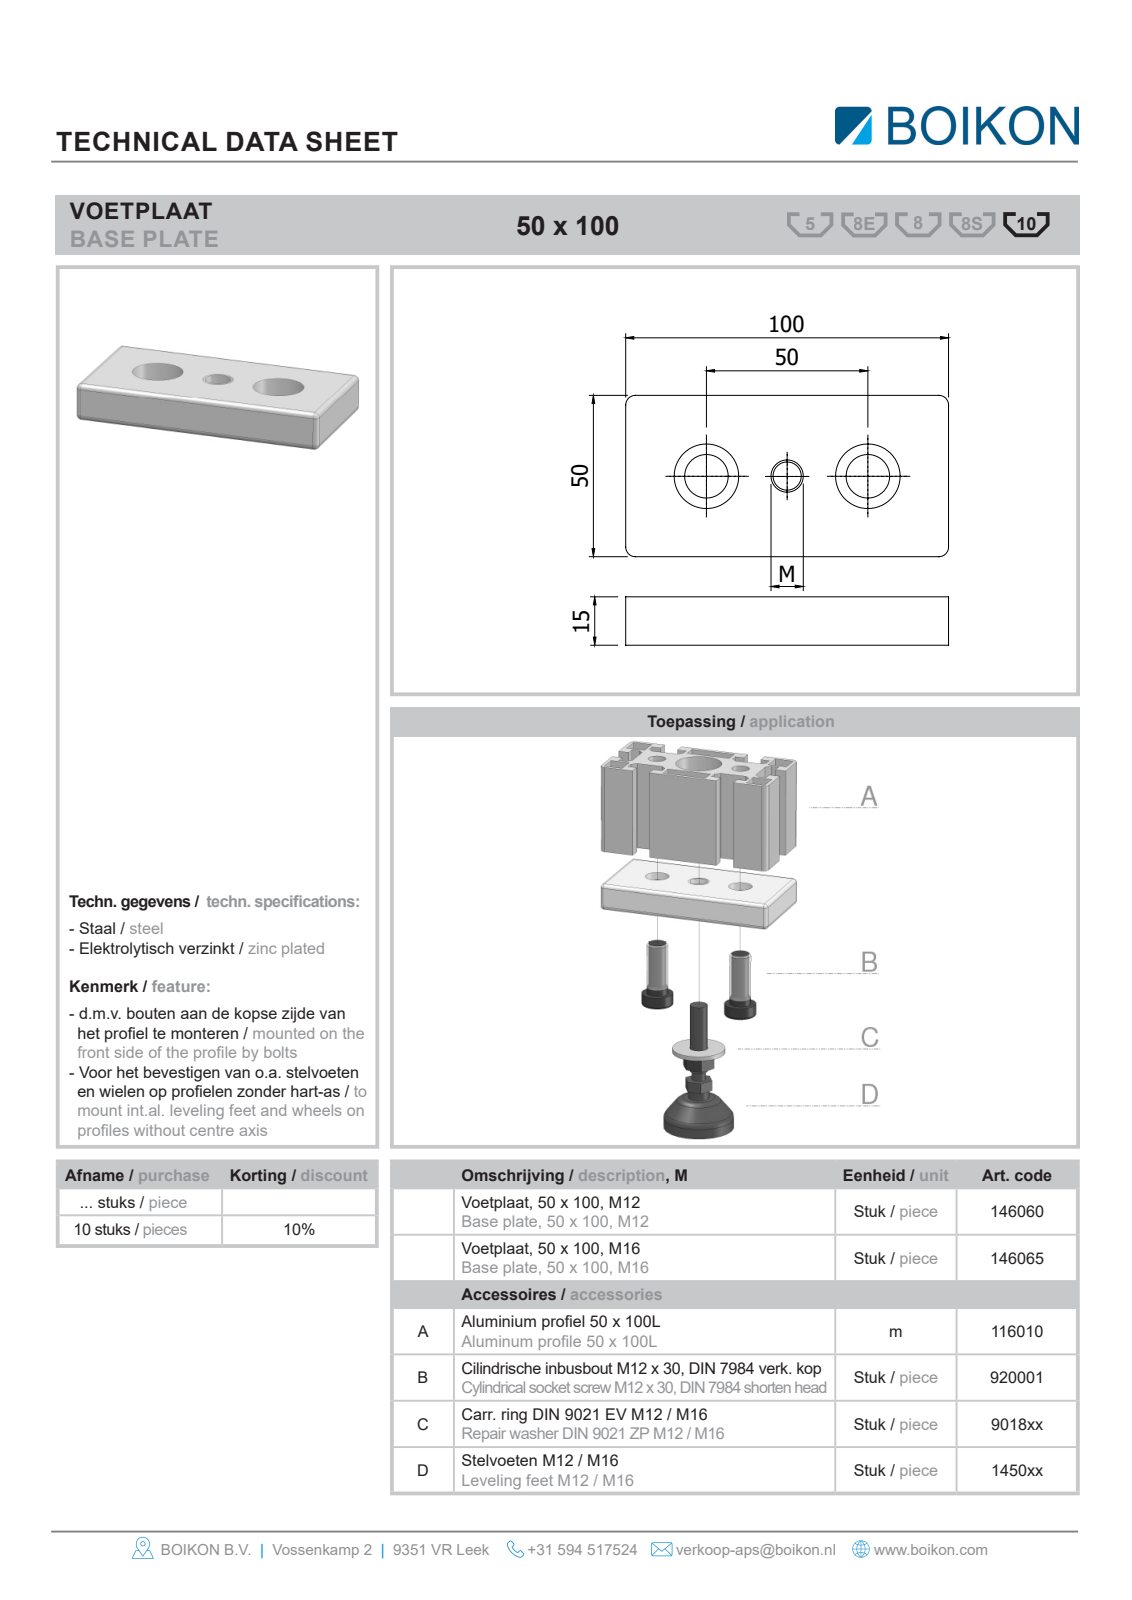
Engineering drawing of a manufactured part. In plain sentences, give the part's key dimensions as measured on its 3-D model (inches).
The part is named "Root; 146060Voetplaat 50x100 M12BOIKON; 920001Cil. inb. M12 x 30, DIN 7984 verk. kopBOIKON0". Its 3-D file was written by "HiCAD 2013 1802.4 Build 509 (AUTOMOTIVE_DESIGN)". It is 3 solids with 57 faces: 40 planar, 11 cylindrical and 6 other. Overall it measures 3.937 by 1.969 by 1.594 inches. Its volume is 4.467 cubic inches and its surface area 30.8 square inches. Round holes: 2 of diameter 0.531, 2 of diameter 0.787, 1 of diameter 0.472. Round bosses or shafts: 2 of diameter 0.709, 2 of diameter 0.472, 2 of diameter 0.388. The main face-to-face distances are 0.591, 1.969, 3.937, 0.177, 0.413, 0.453, 0.276, 0.138, 1.004, 1.181. The hole center spacings are 0.984, 1.969.
